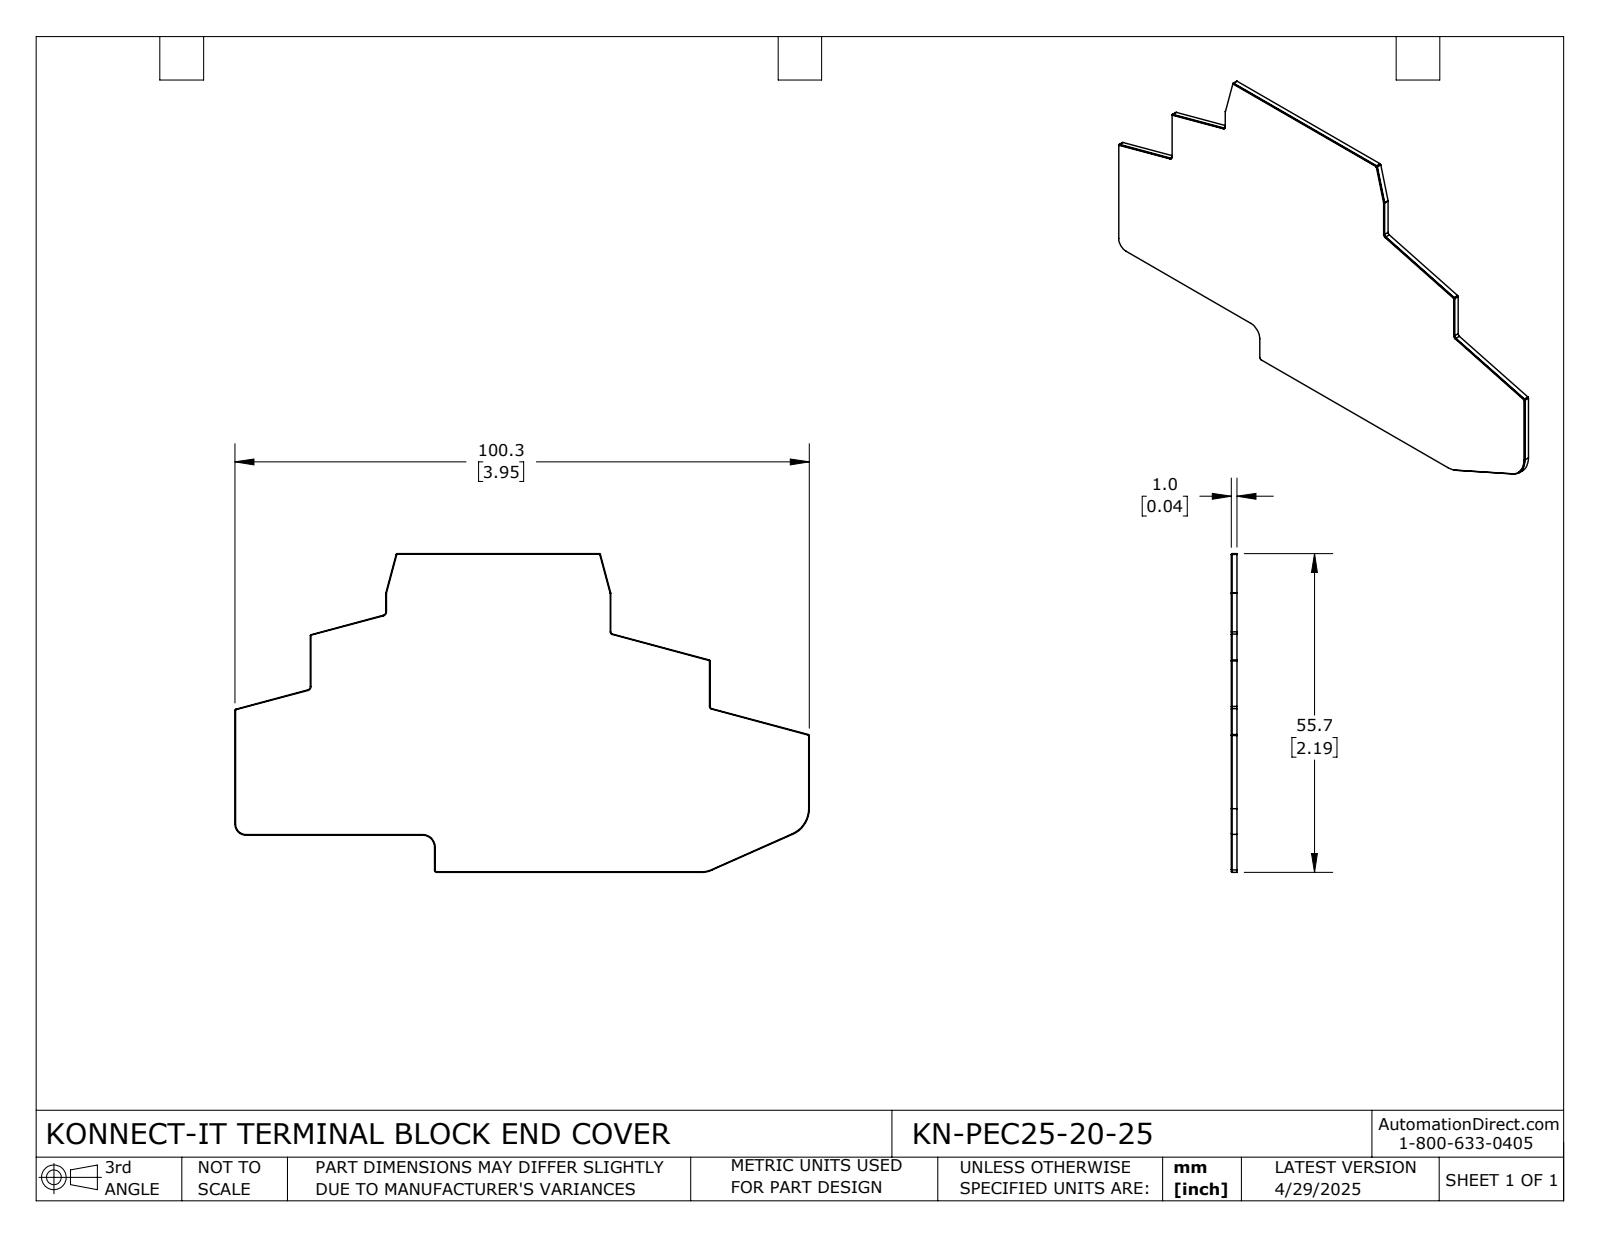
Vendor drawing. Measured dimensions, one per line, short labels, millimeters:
name: KN-PEC25-20-25
written by: SolidWorks 2024 (CONFIG_CONTROL_DESIGN)
unit: mm
bodies: 1 solid, 71 faces (37 planar, 34 cylindrical, 0 other)
size: 100.28 × 55.65 × 1
volume: 3 976 mm³; area: 8 245 mm²
rounds: 8× R0.1, 8× R0.2, 3× R0.4, 2× R0.5, 2× R0.6, 2× R0.7, 2× R4.8, 2× R4.9
face distances: 1, 6.52, 55.66, 0.85, 49.14, 8.09, 9.17, 55.56, 100.27, 49.04
